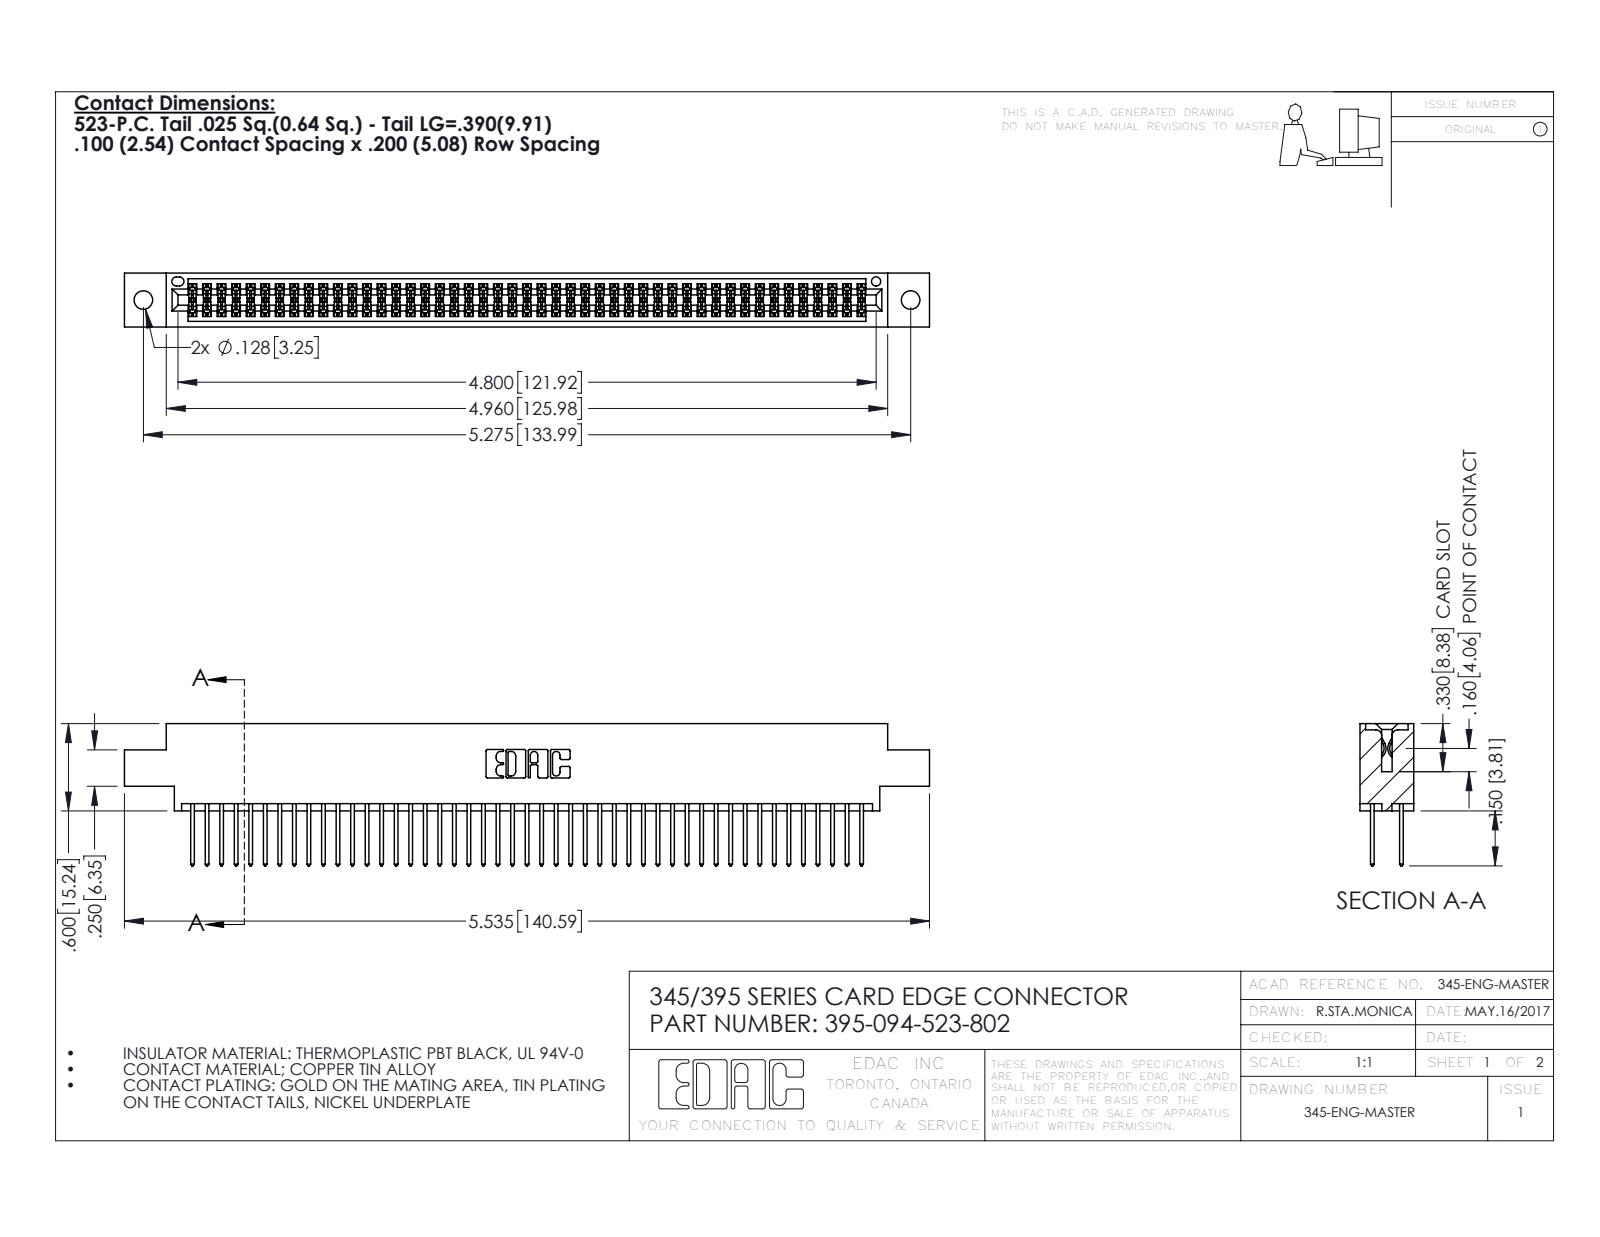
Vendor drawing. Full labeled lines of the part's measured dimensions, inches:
Part name (STEP PRODUCT): 395-094-523-802; 345-292-001_345-293-123; 345 Part_0.170 Offset - 0.128 Dia
STEP written by: SolidWorks 2016 (CONFIG_CONTROL_DESIGN)
Units: inches
Bodies: 95 solids, 4830 faces (3186 planar, 1644 cylindrical, 0 other)
Overall size (bounding box): 5.535 × 0.977 × 0.37
Volume: 0.839 in³ · Surface area: 32.78 in²
Round holes (diameter × count): ⌀0.128 ×2, ⌀0.064 ×1
Partial cylindrical surfaces — rounded edges, fillets, slot ends (radius × count): R0.006 ×141, R0.01 ×94, R0.01 ×22, R0.007 ×6, R0.031 ×6, R0.026 ×3, R0.014 ×2, R0.019 ×2
Main face-to-face distances: 0.298, 0.072, 0.2, 0.098, 0.272, 0.025, 0.37, 0.225, 0.175, 0.149
Hole centre spacings: 0.27, 5.039, 5.275
